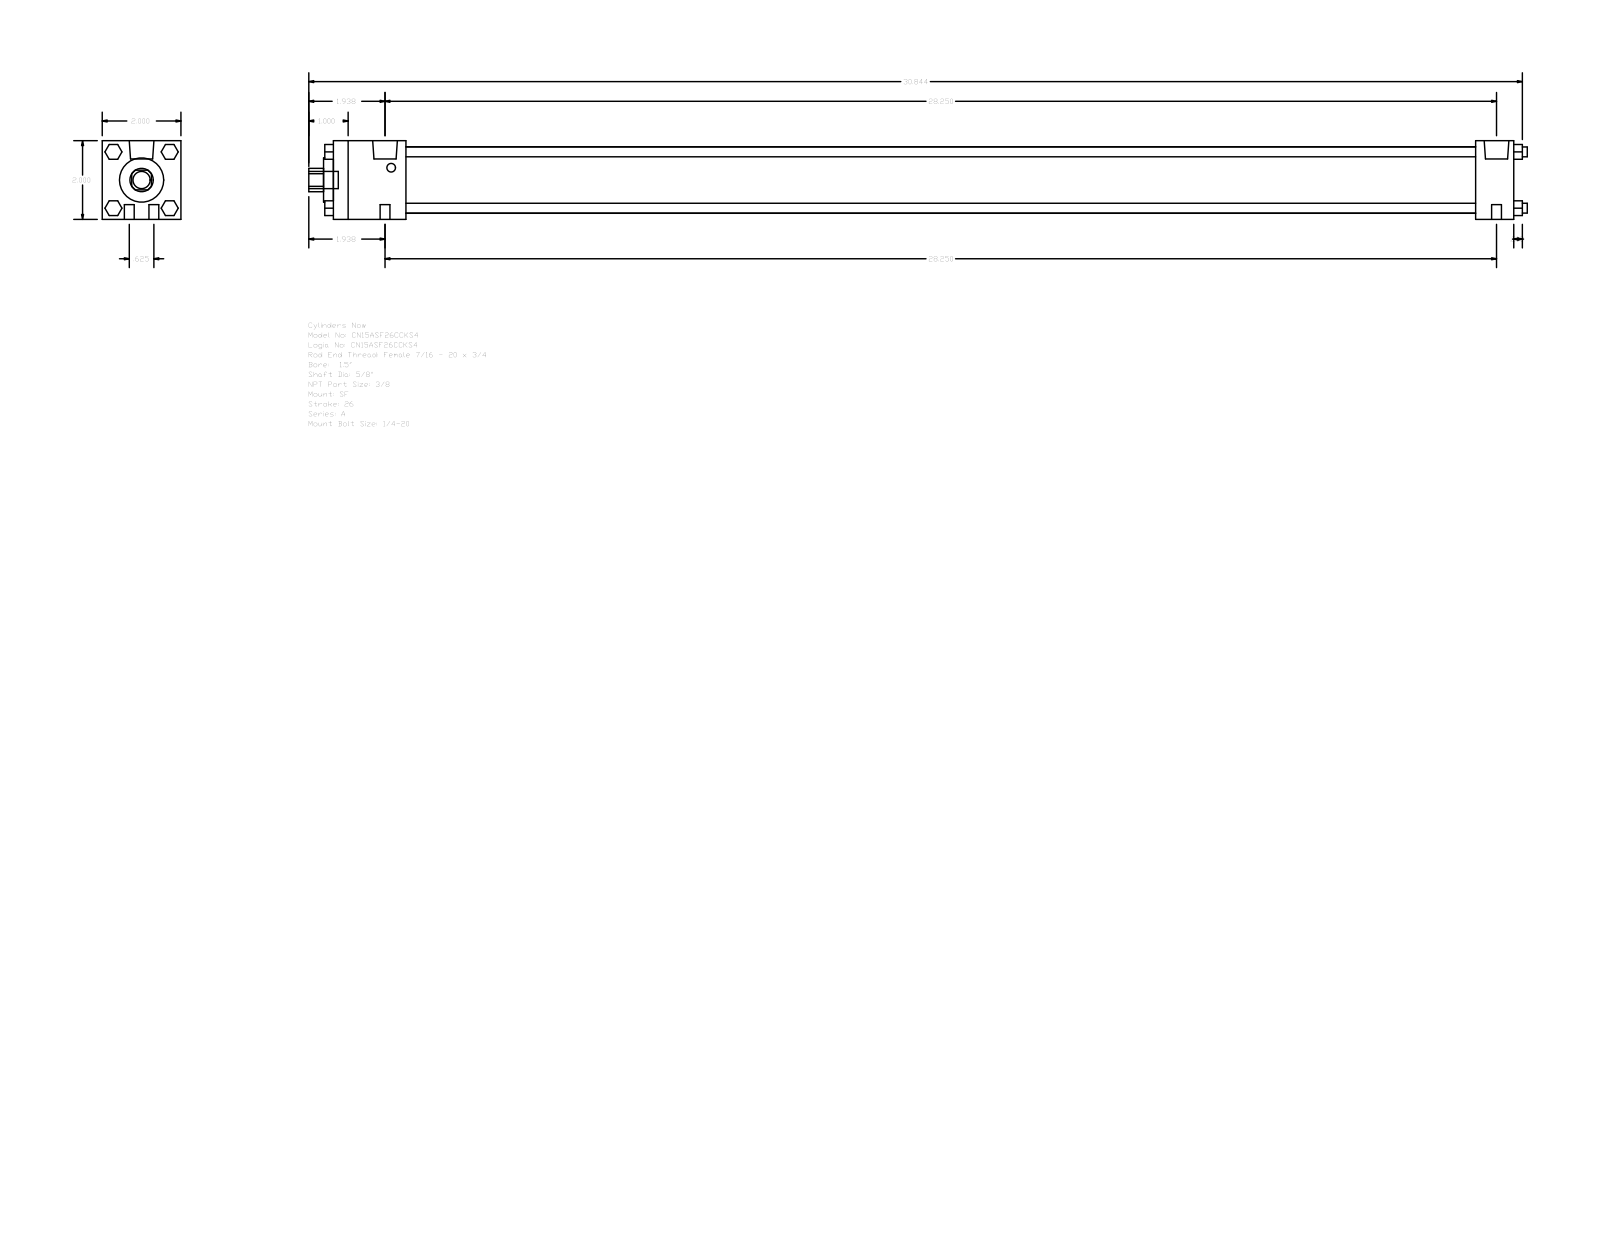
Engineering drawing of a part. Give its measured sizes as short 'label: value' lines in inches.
name: A_SF__0150_0.625
written by: GSSL Pune (CONFIG_CONTROL_DESIGN)
unit: in
bodies: 0 solids, 124 faces (94 planar, 30 cylindrical, 0 other)
size: 30.969 × 2 × 2
holes: 1× ⌀0.625, 1× ⌀1.125, 1× ⌀1.69
bosses: 8× ⌀0.25, 2× ⌀0.627, 2× ⌀0.219, 1× ⌀0.437
rounds: 1× R0.297
face distances: 2, 30, 1.844, 29.031, 27.187, 28.156, 0.969, 0.375, 0.25, 2.094
